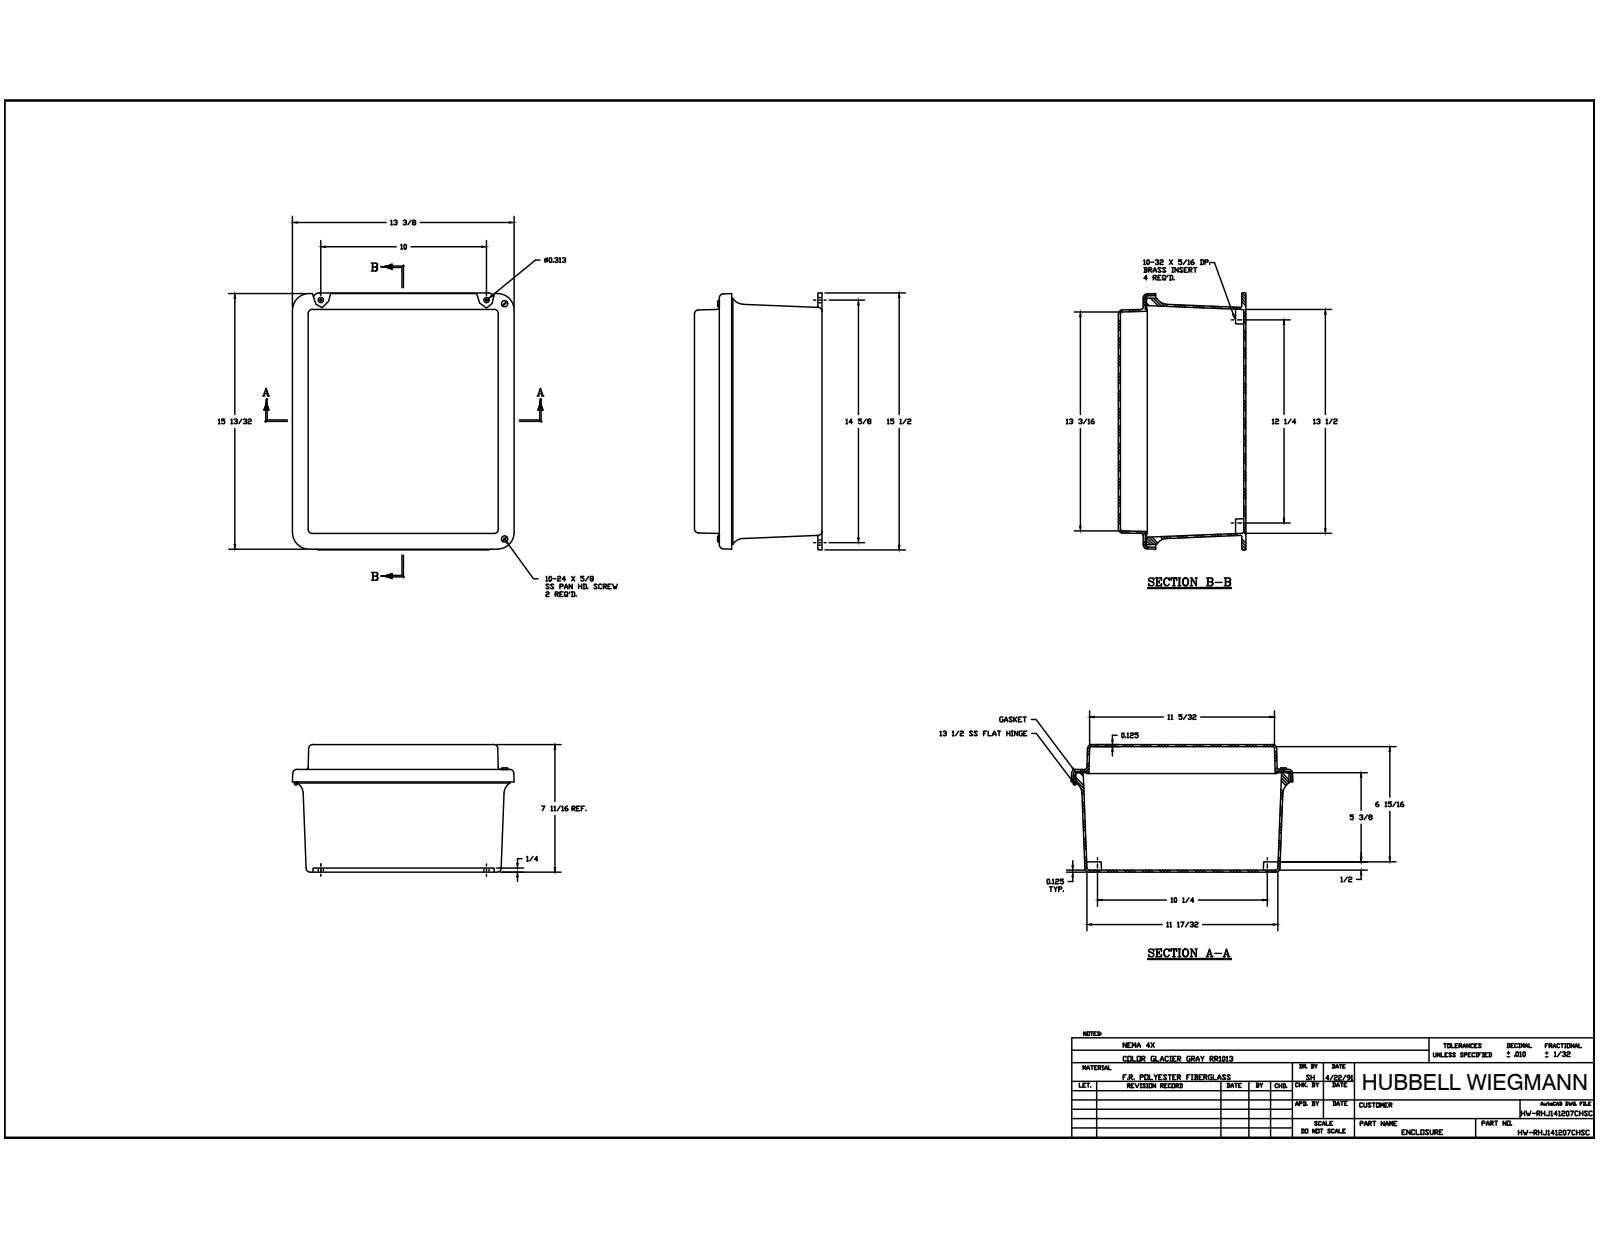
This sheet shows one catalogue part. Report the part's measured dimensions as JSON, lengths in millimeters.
{"part_name": "J1412HW_3; RMINS45821P_267; RMINS45821P_268; RMINS45821P_269 (+8 more)", "step_written_by": "Autodesk Inventor 2014 (AUTOMOTIVE_DESIGN)", "units": "millimeters", "bodies": {"solids": 24, "faces": 925, "planar": 340, "cylindrical": 354, "other": 231}, "overall_size": [393.7, 340.45, 195.65], "volume_mm3": 1947000, "surface_area_mm2": 1104000, "round_holes": [[3.33, 10], [3.56, 10], [3.86, 8], [3.96, 4], [5.54, 4], [3.68, 2], [2.16, 1]], "round_bosses_or_shafts": [[6.35, 10], [3.17, 10], [6.86, 6], [4.83, 2], [3.97, 2], [3.94, 1]], "partial_cylinders_radius": [[0.79, 20], [3.17, 20], [6.35, 20], [5.08, 4], [7.18, 4], [9.53, 4], [19.05, 4], [1.6, 2]], "face_to_face_distances": [3.18, 3.17, 189.3, 192.48, 195.65, 192.47, 38.1, 151.2, 154.38, 41.27], "hole_center_spacings": [82.55, 165.1, 247.65, 6.35, 76.2, 34.8, 158.75, 286.01]}
